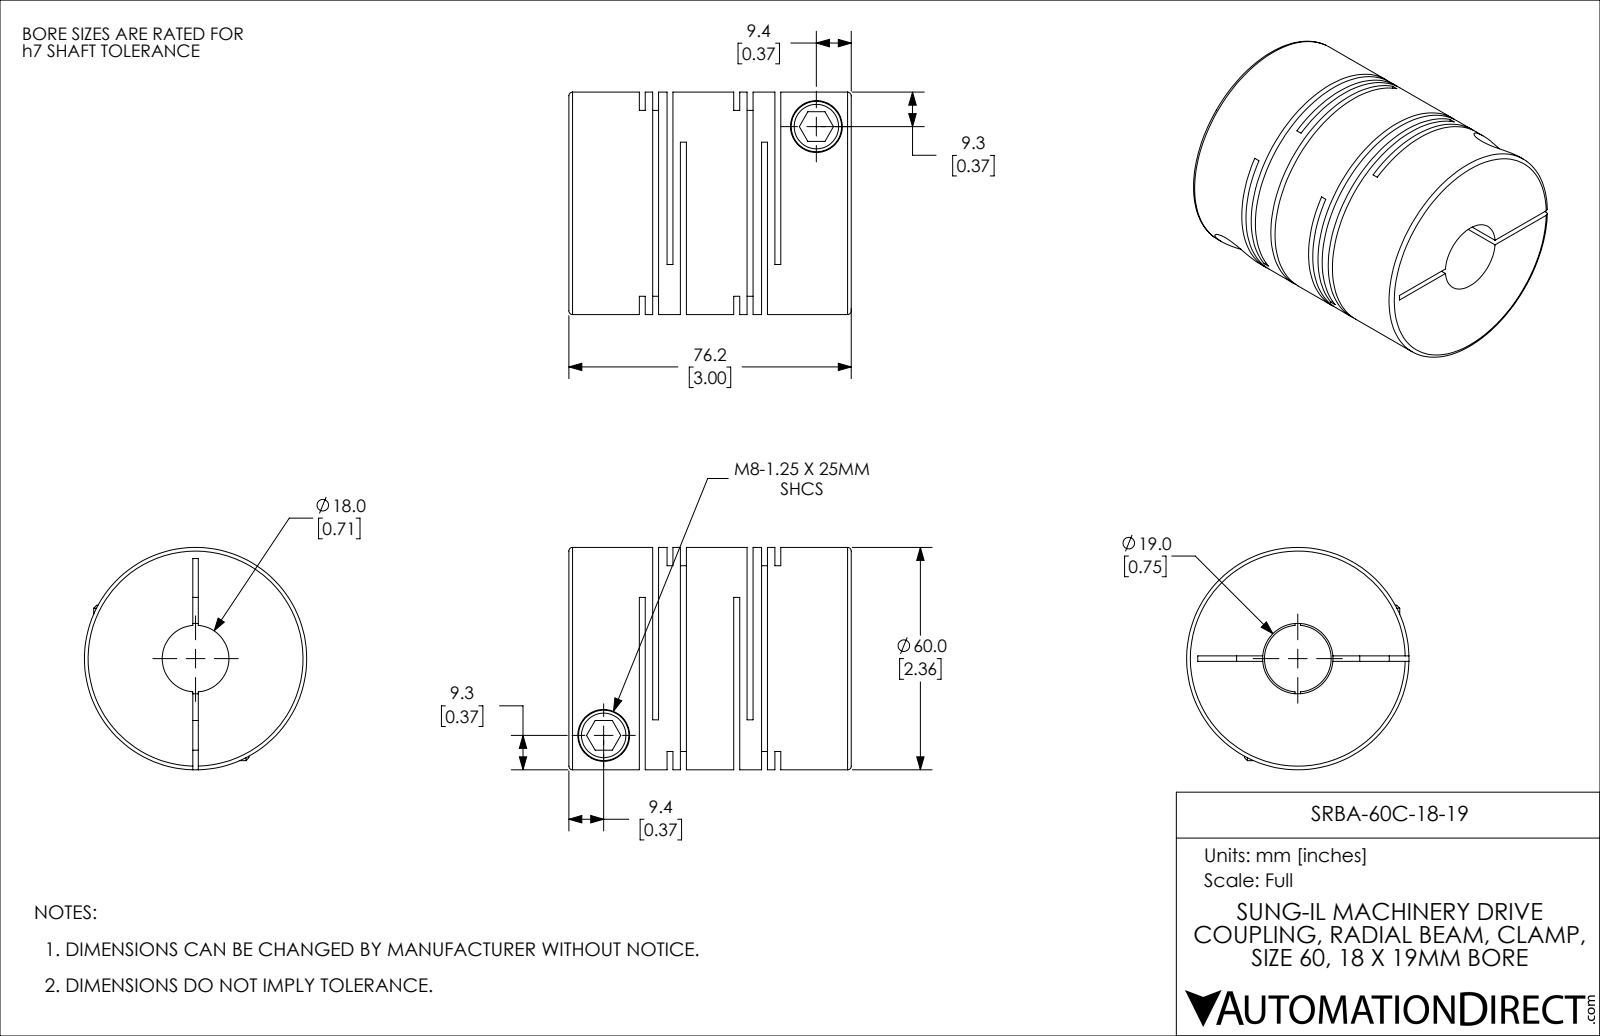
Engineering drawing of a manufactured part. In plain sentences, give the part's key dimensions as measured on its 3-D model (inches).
The part is named "SRBA-60C-18-19". Its 3-D file was written by "SolidWorks 2021 (CONFIG_CONTROL_DESIGN)". It is 1 solid with 115 faces: 60 planar, 42 cylindrical and 13 other. Overall it measures 3 by 2.362 by 2.362 inches. Its volume is 9.928 cubic inches and its surface area 92.35 square inches. Round holes: 2 of diameter 0.315, 2 of diameter 0.551, 1 of diameter 0.709, 1 of diameter 0.748. Round bosses or shafts: 2 of diameter 0.535, 1 of diameter 2.362. The main face-to-face distances are 0.063, 0.142, 0.295, 1.004, 1.299, 1.067, 0.709, 0.079, 0.232, 0.941.
